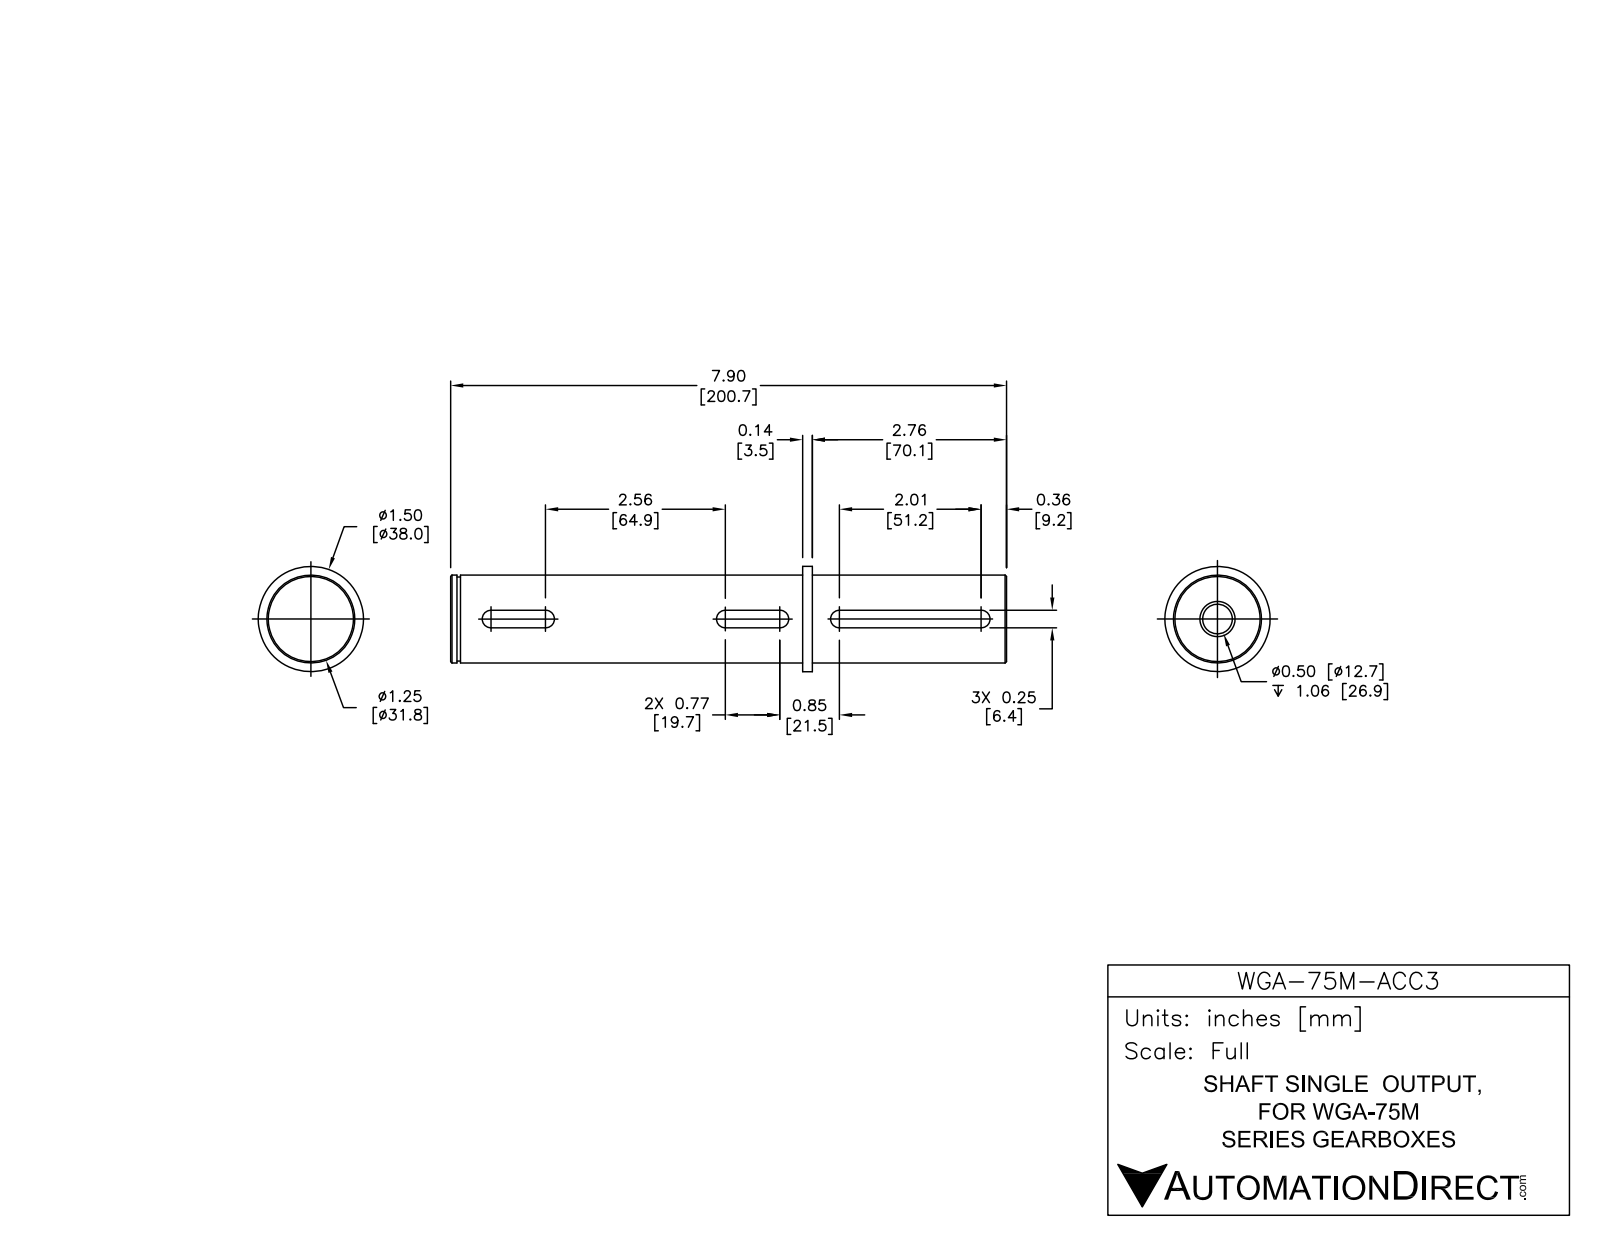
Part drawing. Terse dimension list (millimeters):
name: WGA-75M-ACC3
written by: SolidWorks 2014 (AUTOMOTIVE_DESIGN)
unit: mm
bodies: 1 solid, 42 faces (16 planar, 20 cylindrical, 6 other)
size: 200.7 × 38 × 38
volume: 153 100 mm³; area: 24 660 mm²
holes: 1× ⌀10.7, 1× ⌀12.7
bosses: 1× ⌀38, 1× ⌀31.8, 1× ⌀30.3
rounds: 6× R3.2
face distances: 200.7, 127.1, 73.6, 130.6, 3.5, 70.1, 6.4, 2.3, 124.8, 128.3
